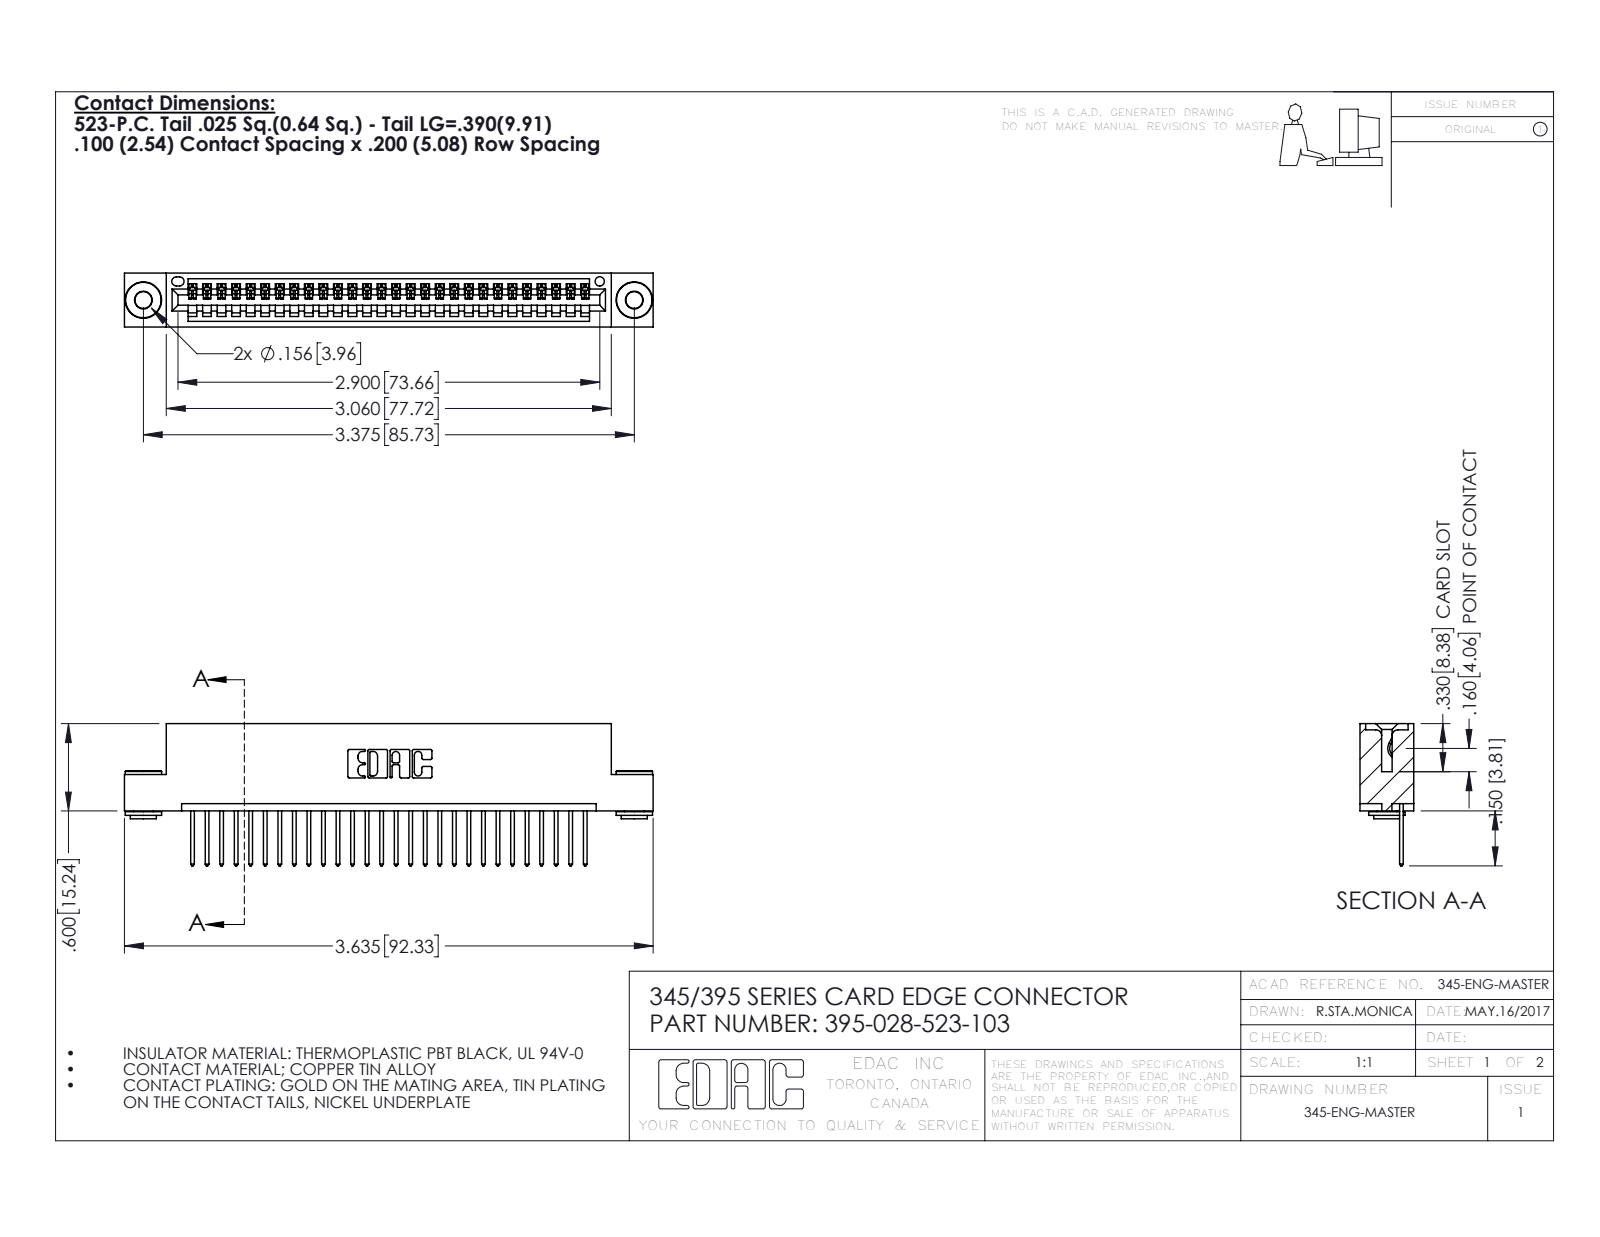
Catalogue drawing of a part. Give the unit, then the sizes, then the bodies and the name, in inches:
Units: inches
Overall size (bounding box): 3.635 × 0.977 × 0.37
Round holes (diameter × count): ⌀0.116 ×2, ⌀0.156 ×2, ⌀0.064 ×1
Round bosses / shafts (diameter × count): ⌀0.25 ×2, ⌀0.18 ×2, ⌀0.136 ×2
Partial cylindrical surfaces — rounded edges, fillets, slot ends (radius × count): R0.006 ×56, R0.01 ×56, R0.01 ×22, R0.007 ×6, R0.031 ×6, R0.026 ×3, R0.031 ×2, R0.04 ×2
Main face-to-face distances: 0.072, 0.298, 0.2, 0.37, 0.025, 0.098, 0.272, 0.225, 0.149, 0.072
Hole centre spacings: 0.27, 3.14, 3.375
Volume: 0.529 in³ · Surface area: 17.93 in²
Bodies: 31 solids, 1788 faces (1210 planar, 570 cylindrical, 8 other)
Part name (STEP PRODUCT): 345 Part_Flush Mounting Lugs - 0.156 Dia-TH; 395-028-523-103; 345-250-002_345-250-002-102; 345-292-001_345-293-123
STEP written by: SolidWorks 2016 (CONFIG_CONTROL_DESIGN)
